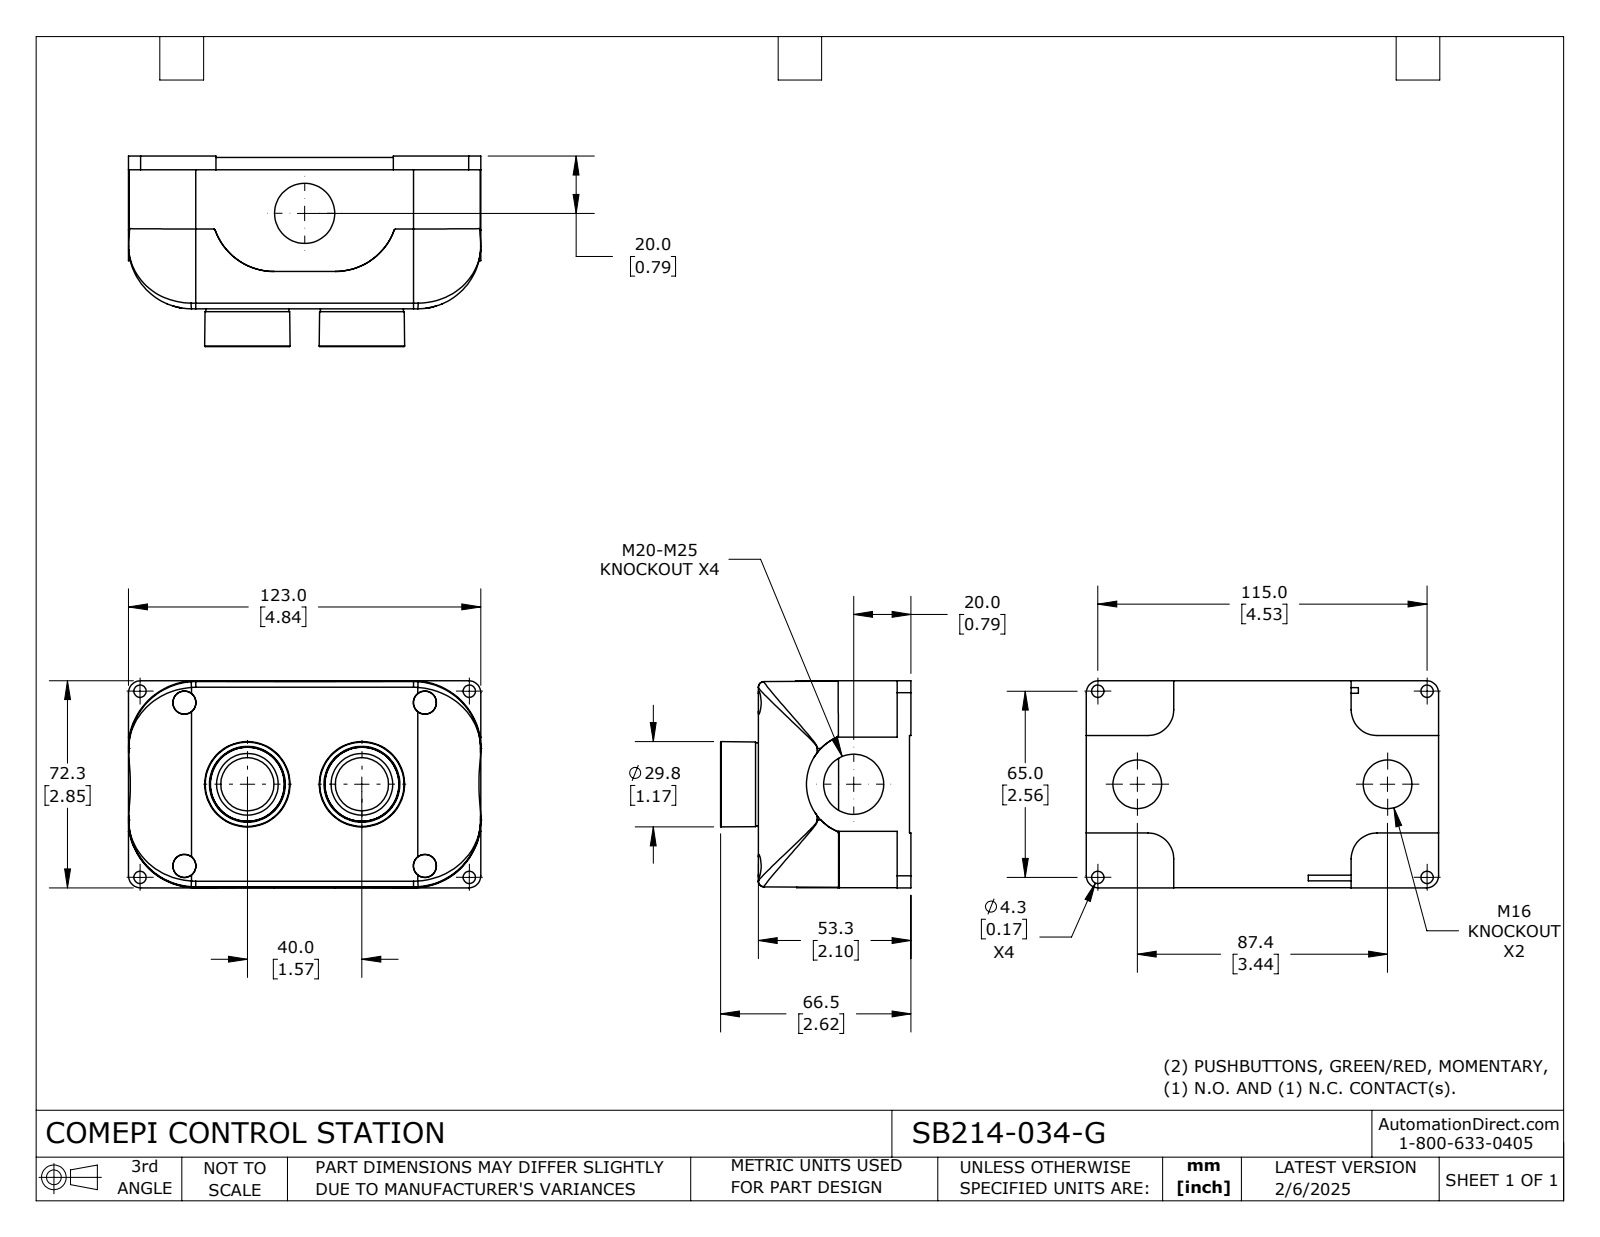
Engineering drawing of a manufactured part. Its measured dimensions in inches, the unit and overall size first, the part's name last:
Units: inches
Overall size (bounding box): 4.843 × 2.846 × 2.618
Round holes (diameter × count): ⌀0.169 ×4, ⌀0.531 ×2, ⌀0.669 ×2, ⌀0.827 ×2, ⌀0.854 ×2
Round bosses / shafts (diameter × count): ⌀1.142 ×2, ⌀1.016 ×2, ⌀0.748 ×2, ⌀0.63 ×2, ⌀0.614 ×2
Partial cylindrical surfaces — rounded edges, fillets, slot ends (radius × count): R0.01 ×4, R0.035 ×4, R0.079 ×4, R0.157 ×4, R0.354 ×4, R0.38 ×4, R0.866 ×4, R0.93 ×4
Main face-to-face distances: 0.098, 2.079, 1.98, 0.118, 1.102, 0.976, 0.878, 2.098, 0.02, 2.618
Hole centre spacings: 1.39, 1.954, 3.309, 4.185, 0.933, 2.508, 2.559, 4.528
Volume: 16.11 in³ · Surface area: 123.7 in²
Bodies: 8 solids, 427 faces (185 planar, 106 cylindrical, 136 other)
Part name (STEP PRODUCT): SB214-034-G
STEP written by: SolidWorks 2024 (CONFIG_CONTROL_DESIGN)
